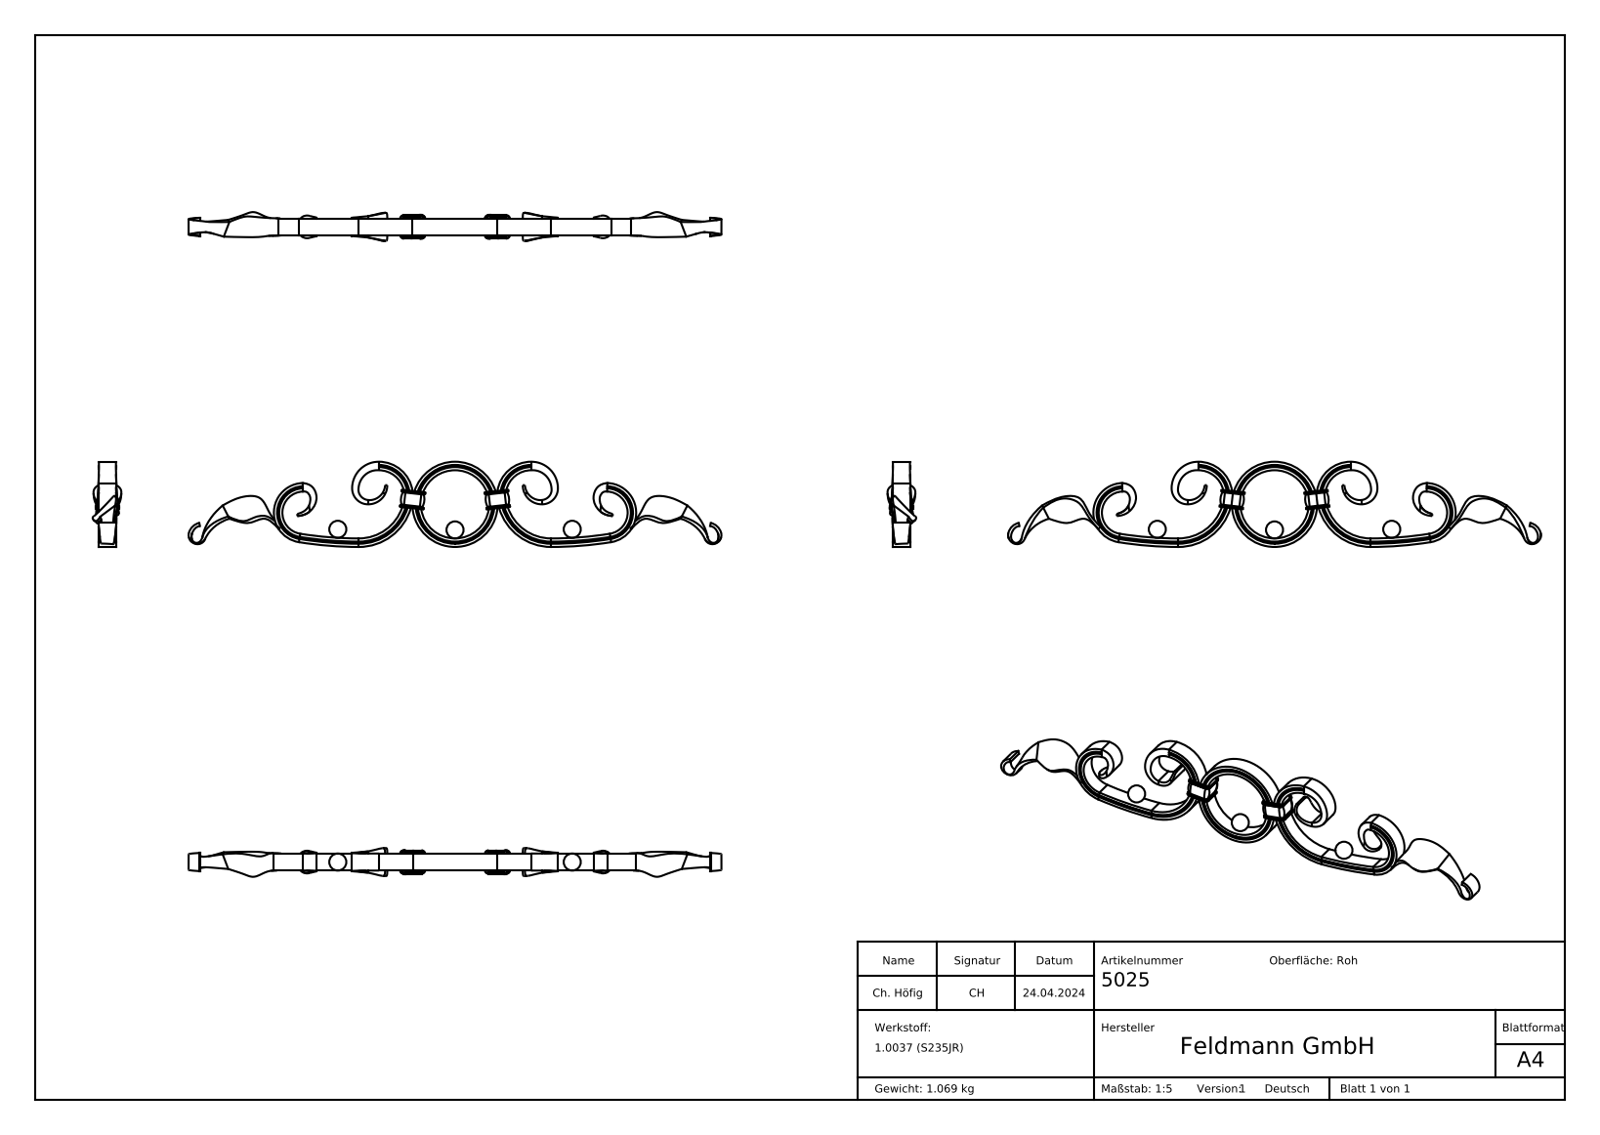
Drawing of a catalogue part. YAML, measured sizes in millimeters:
part_name: "5025"
step_written_by: "SolidWorks 2018 (CONFIG_CONTROL_DESIGN)"
units: millimeters
bodies: {solids: 8, faces: 675, planar: 248, cylindrical: 151, other: 276}
overall_size: [500.04, 80, 27.06]
volume: 137023
surface_area: 64020
round_holes:
  - {diameter: 64, count: 1}
round_bosses_or_shafts:
  - {diameter: 80, count: 1}
partial_cylinders:
  - {radius: 0.5, count: 76}
  - {radius: 3.5, count: 8}
  - {radius: 14.83, count: 8}
  - {radius: 19.93, count: 2}
  - {radius: 24, count: 2}
  - {radius: 27.93, count: 2}
  - {radius: 32, count: 2}
  - {radius: 42.83, count: 2}
face_to_face_distances: [16, 16.02, 16.01, 3, 19, 1.5, 14.51, 19.02, 22, 13]
